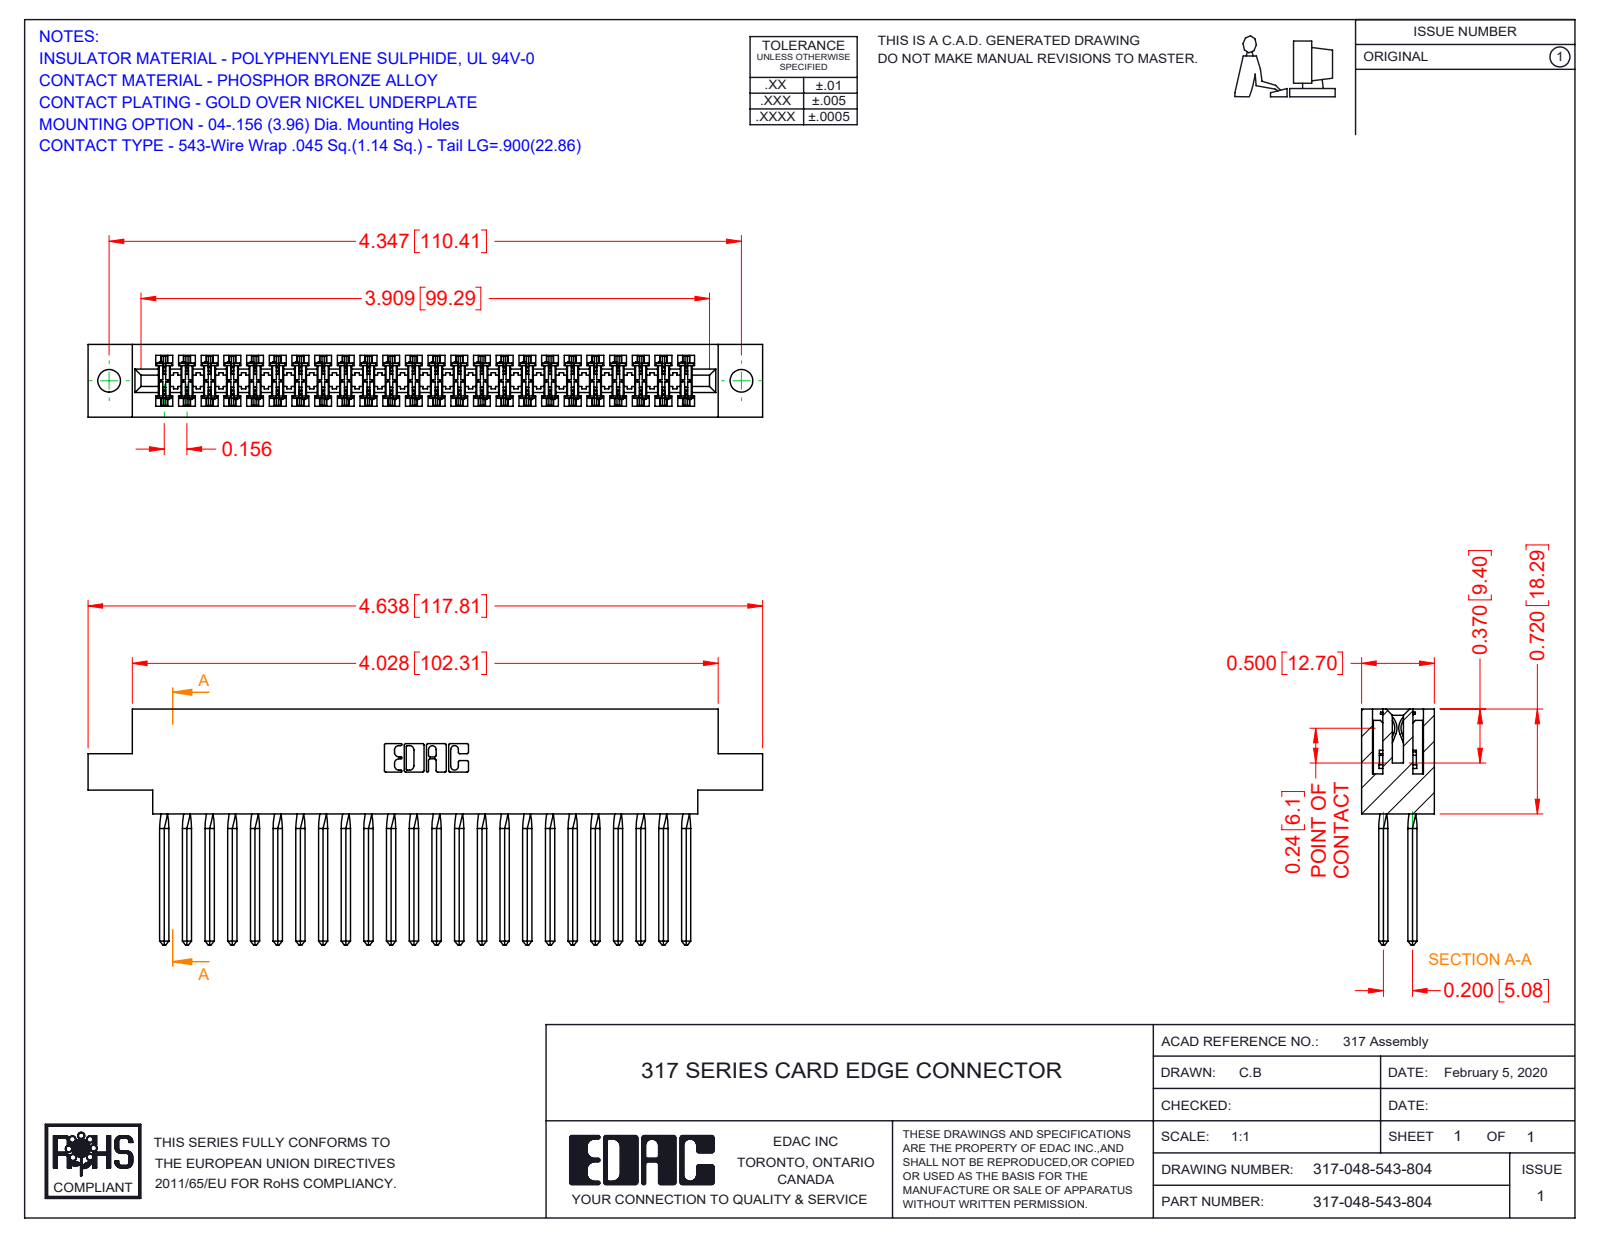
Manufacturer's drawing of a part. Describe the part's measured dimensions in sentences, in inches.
The part is named "317-290-001_543; 317-048-543-804; 317 Part_.156 Dia - TH". Its 3-D file was written by "SolidWorks 2016 (CONFIG_CONTROL_DESIGN)". It is 49 solids with 4374 faces: 3562 planar, 620 cylindrical and 192 other. Overall it measures 4.638 by 1.62 by 0.5 inches. Its volume is 1.179 cubic inches and its surface area 44.05 square inches. Round holes: 2 of diameter 0.156. Partial cylindrical surfaces (rounded edges, fillets, slot ends): 96 of radius 0.015, 22 of radius 0.01, 6 of radius 0.007, 6 of radius 0.031, 3 of radius 0.026, 2 of radius 0.095, 2 of radius 0.1, 2 of radius 0.11. The main face-to-face distances are 0.5, 0.075, 0.425, 0.11, 0.35, 0.195, 0.22, 0.094, 0.72, 0.2. The hole center spacings are 4.347.
